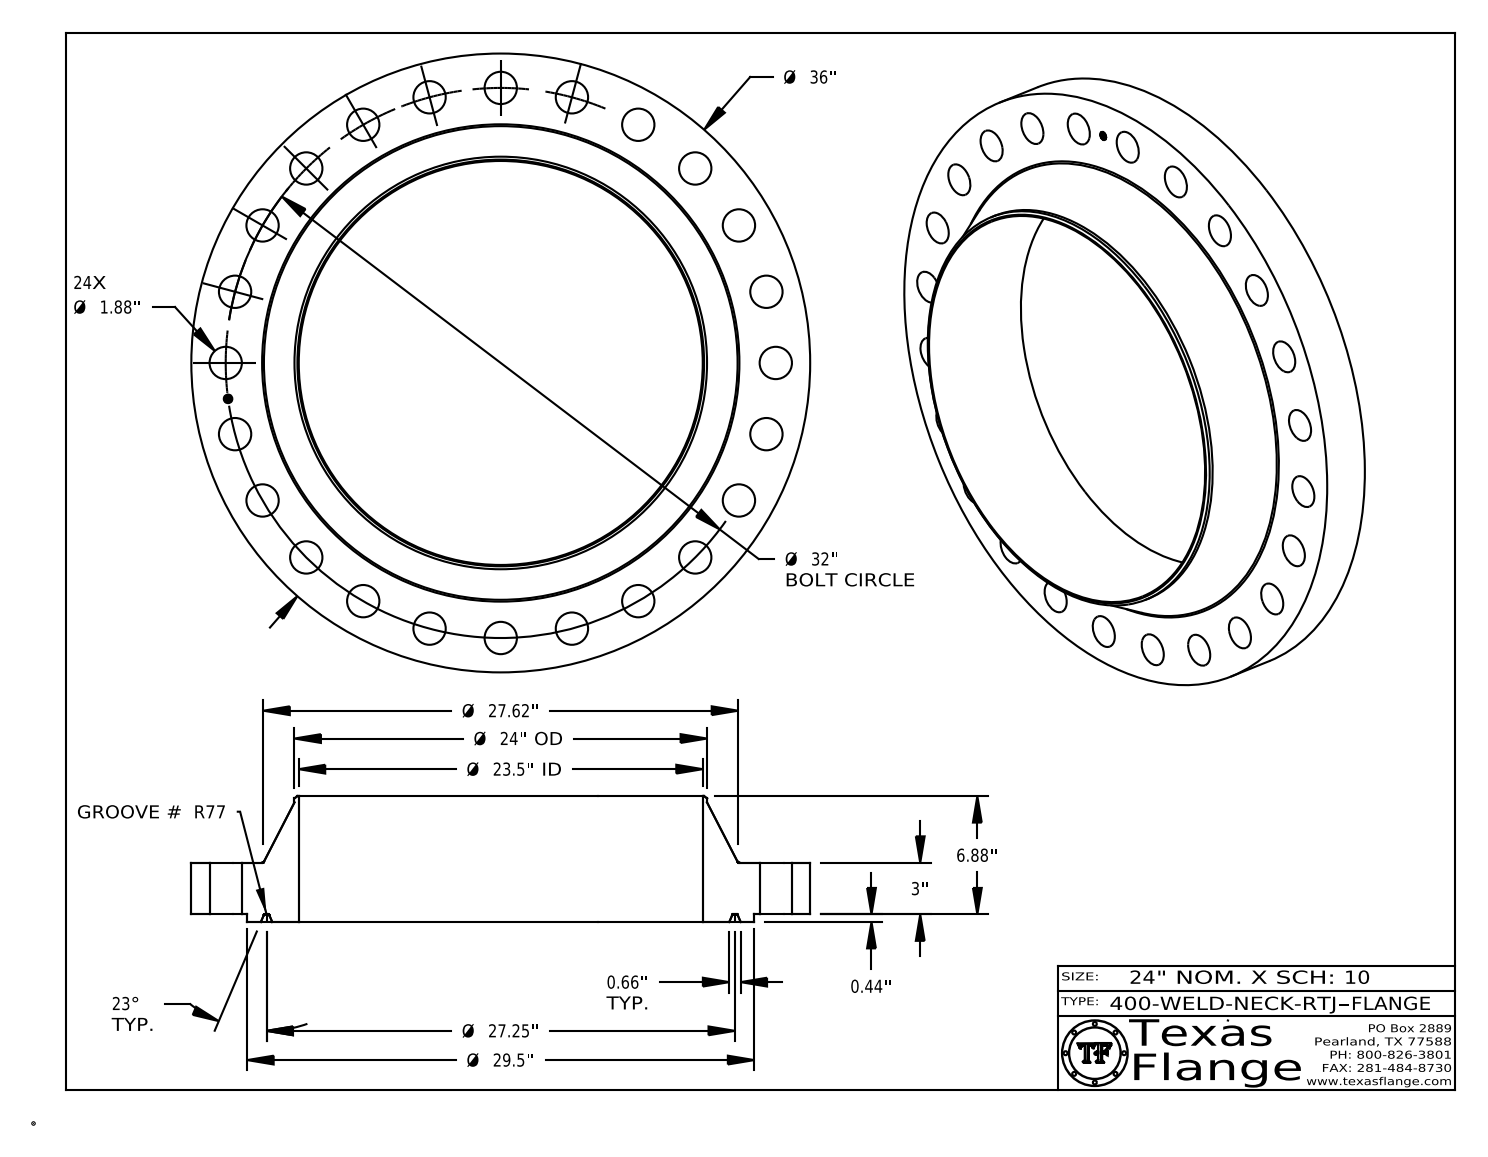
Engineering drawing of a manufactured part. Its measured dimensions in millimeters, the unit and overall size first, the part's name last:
Units: millimetres
Overall size (bounding box): 914.4 × 914.4 × 185.9
Round holes (diameter × count): ⌀47.8 ×24, ⌀12.6 ×1, ⌀596.9 ×1
Round bosses / shafts (diameter × count): ⌀0.8 ×8, ⌀914.4 ×1, ⌀749.3 ×1, ⌀609.6 ×1, ⌀9.9 ×1
Main face-to-face distances: 76.2, 11.1, 87.3, 185.9, 174.8, 98.6, 86.9, 75.8, 0.4, 98.9
Hole centre spacings: 406.4, 785.1, 106.1, 210.4, 311, 494.8, 574.7, 644.8
Volume: 32 250 000 mm³ · Surface area: 1 692 000 mm²
Bodies: 1 solid, 461 faces (371 planar, 76 cylindrical, 14 other)
Part name (STEP PRODUCT): 400-WELD-NECK-RTJ
STEP written by: CATIA V5 STEP AP214 (AUTOMOTIVE_DESIGN)
